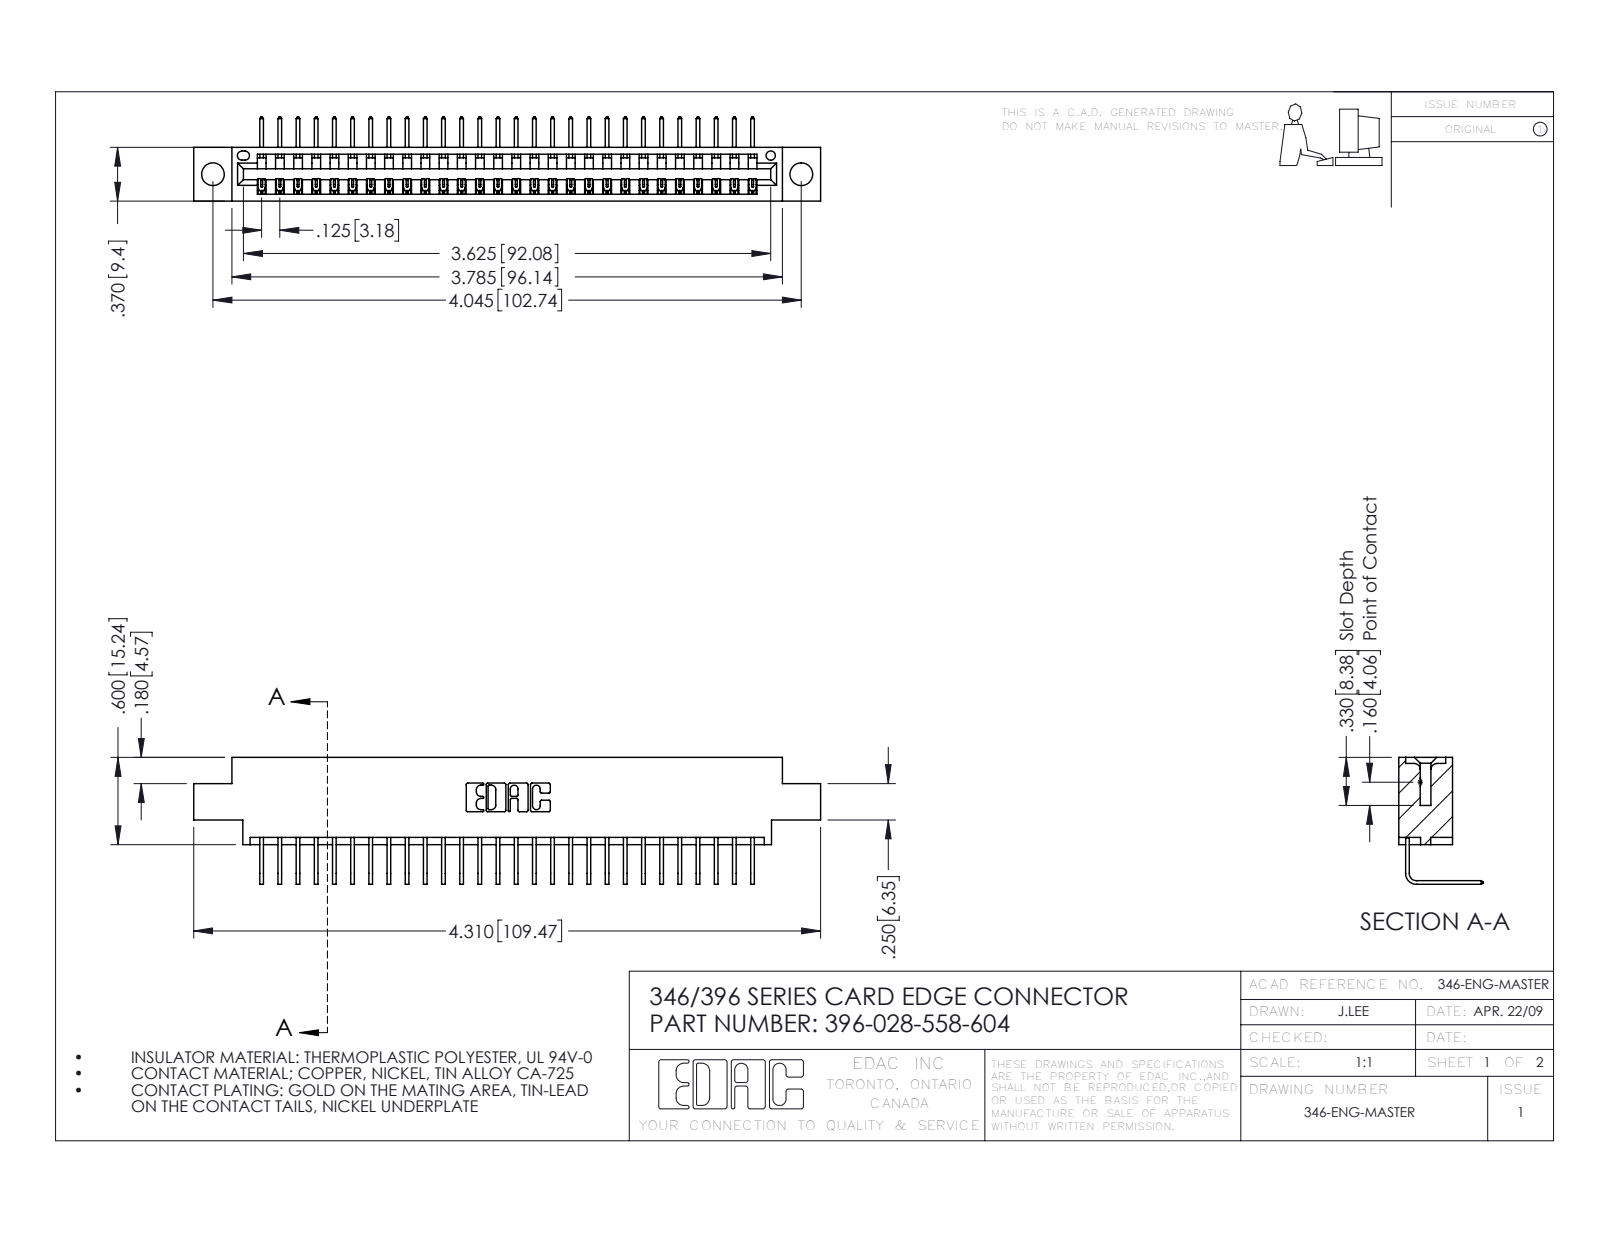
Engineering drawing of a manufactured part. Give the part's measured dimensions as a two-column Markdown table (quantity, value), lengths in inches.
| quantity | value |
| --- | --- |
| part name | 345-292-001_558 Tail - 2; 346 Part_0.170 Offset - 0.156 Dia-TH; 396-028-558-604 |
| STEP written by | SolidWorks 2016 (CONFIG_CONTROL_DESIGN) |
| units | inches |
| bodies | 29 solids, 1806 faces (1256 planar, 550 cylindrical, 0 other) |
| overall size | 4.31 × 0.873 × 0.58 |
| volume | 0.624 in³ |
| surface area | 20.4 in² |
| round holes (diameter × count) | 0.156 × 2, 0.064 × 1 |
| partial cylindrical surfaces (radius × count) | 0.006 × 56, 0.01 × 22, 0.007 × 6, 0.031 × 6, 0.026 × 3, 0.031 × 2, 0.04 × 2, 0.014 × 1 |
| main face-to-face distances | 0.322, 0.048, 0.37, 0.25, 0.298, 0.025, 0.072, 0.148, 0.222, 0.1 |
| hole center spacings | 0.246, 3.837, 4.045 |
